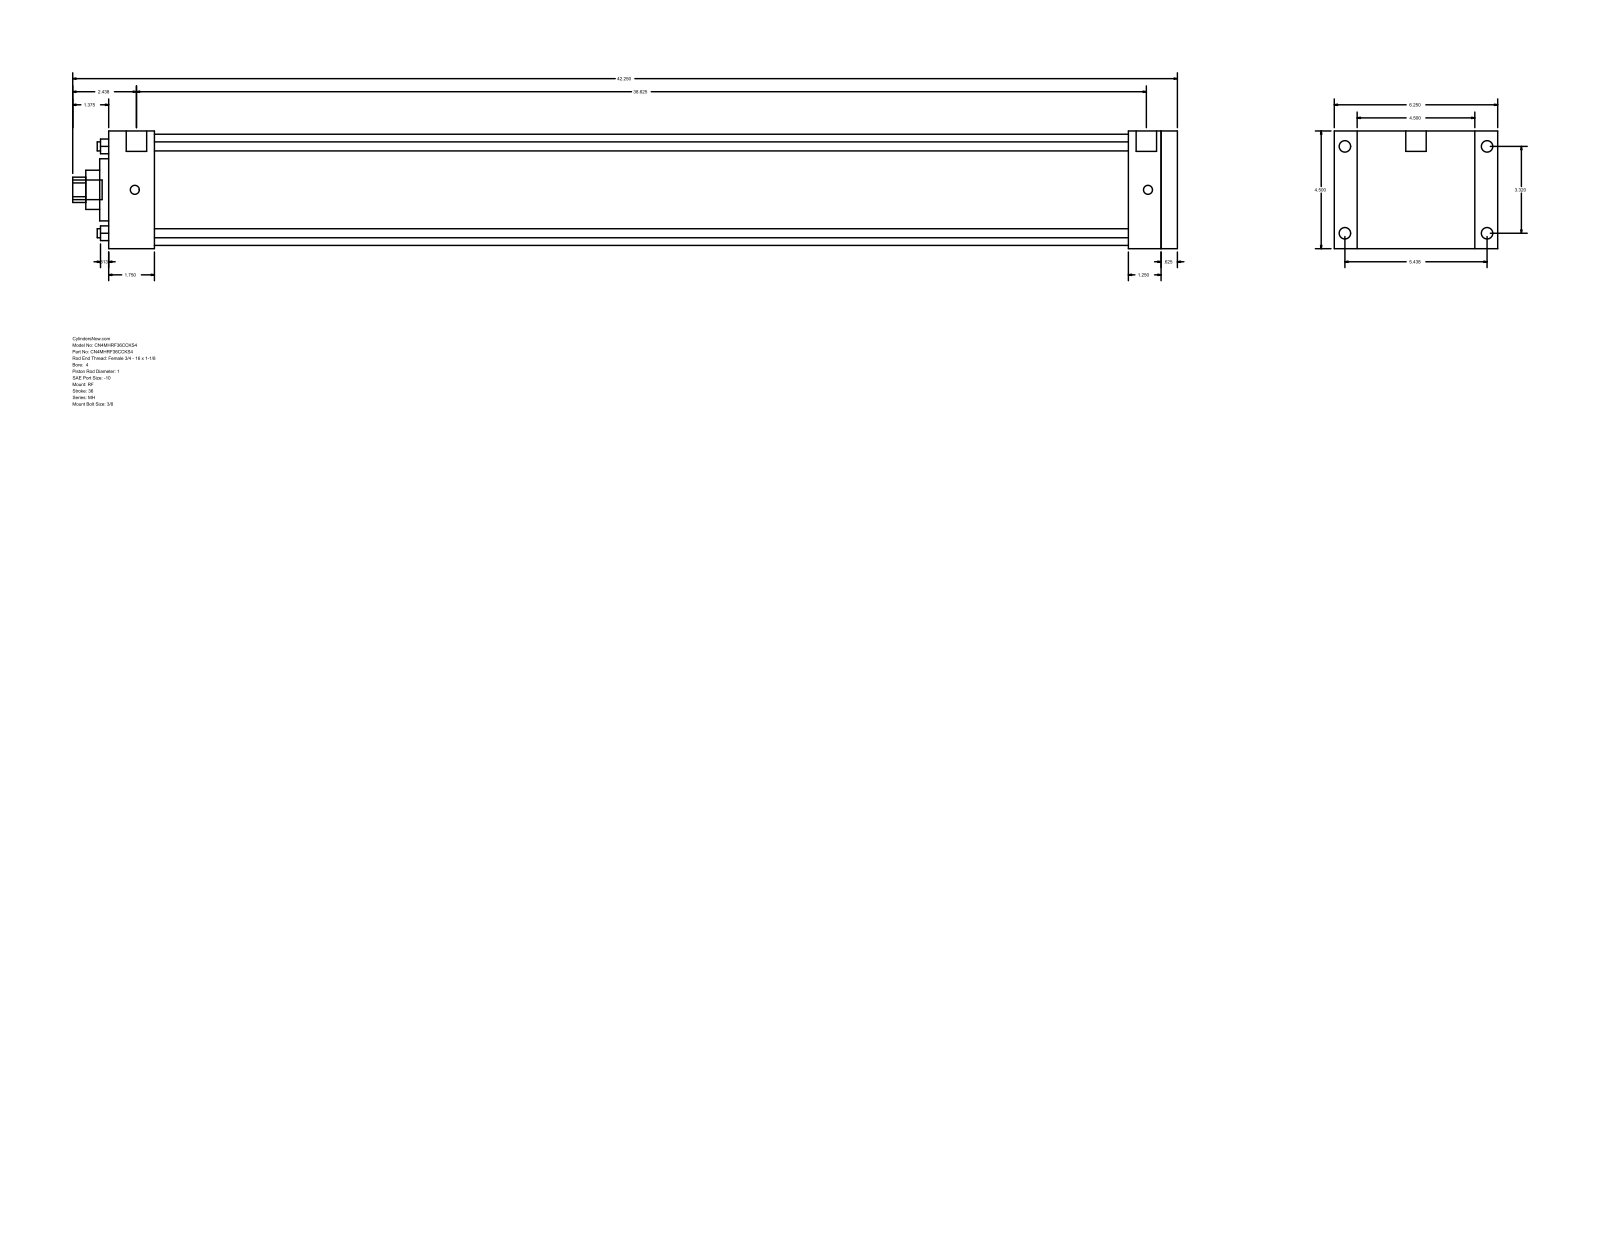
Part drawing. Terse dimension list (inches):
name: MH_RF__0400_1
written by: GSSL Pune (CONFIG_CONTROL_DESIGN)
unit: in
bodies: 0 solids, 94 faces (65 planar, 29 cylindrical, 0 other)
size: 42.25 × 6.25 × 4.5
holes: 4× ⌀0.345, 1× ⌀1, 1× ⌀1.5, 1× ⌀2.375, 1× ⌀4.25
bosses: 4× ⌀0.438, 4× ⌀0.344, 2× ⌀0.781, 1× ⌀0.75
rounds: 1× R0.484
face distances: 4.5, 40.875, 0.625, 40.25, 1.75, 38.5, 39.125, 39, 37.25, 1.25
hole spacings: 2.347, 3.32, 4.695
